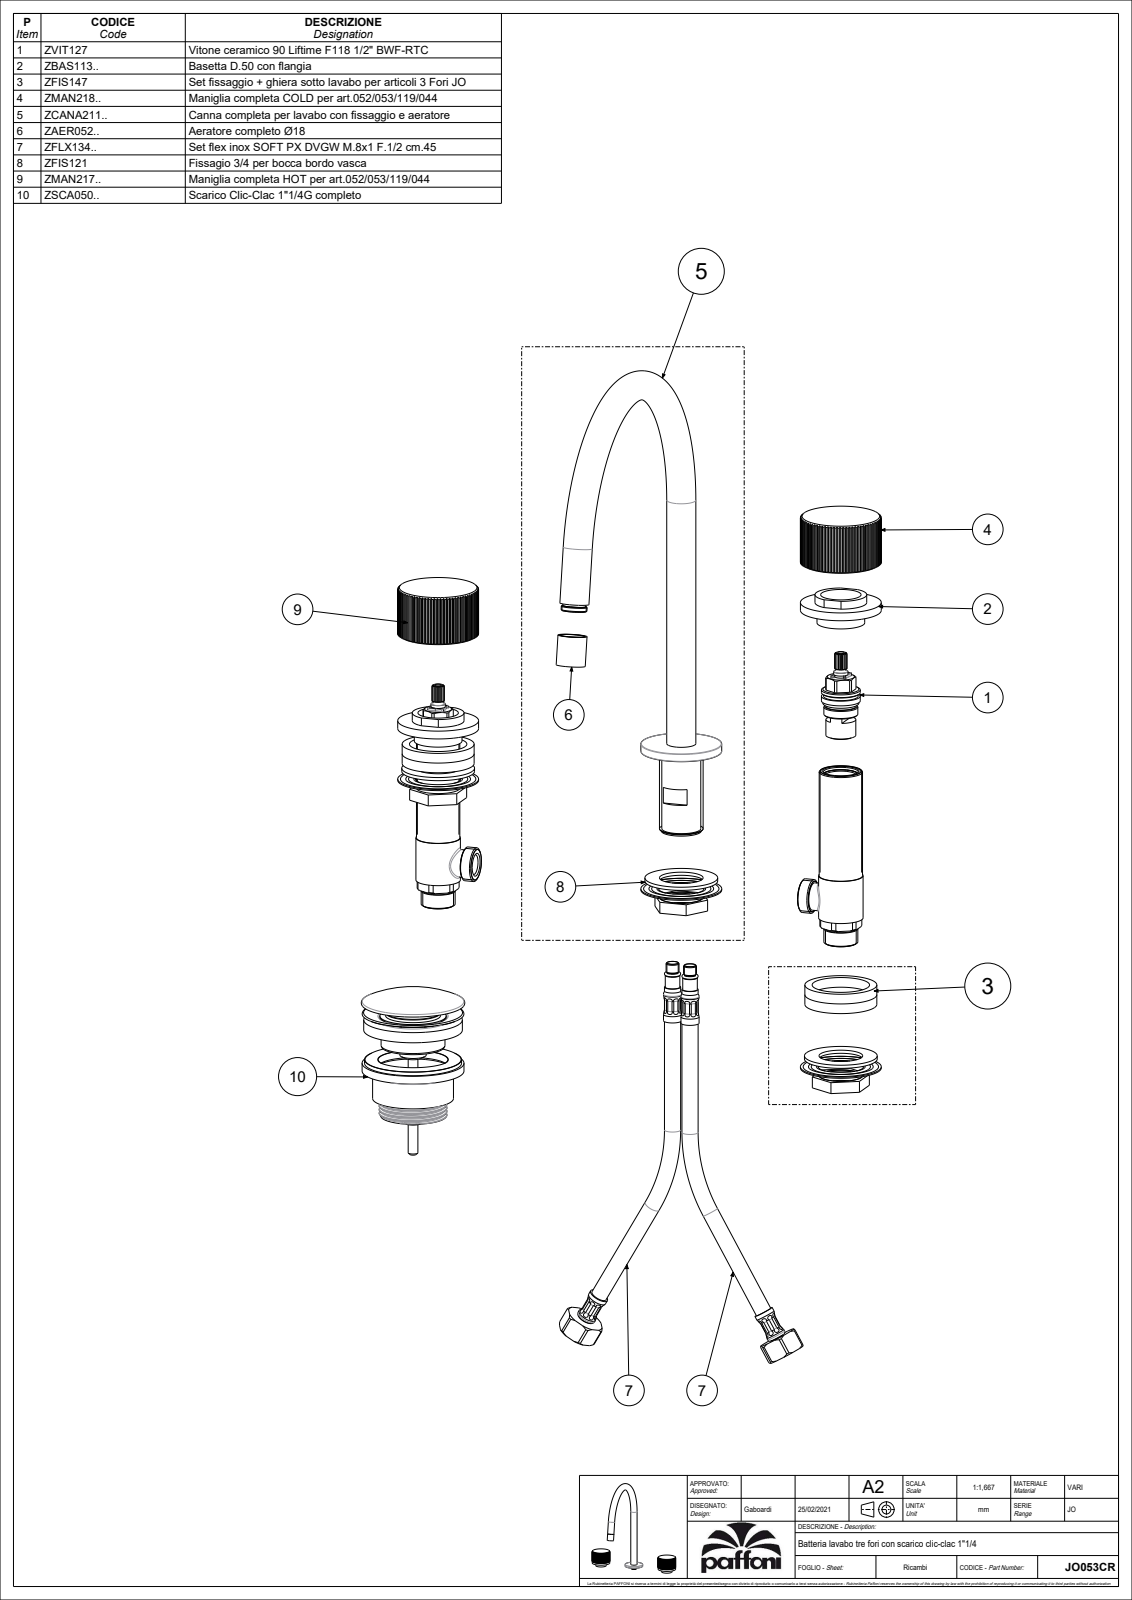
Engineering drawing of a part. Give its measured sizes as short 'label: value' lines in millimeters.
name: JO052CR
written by: CREO PARAMETRIC BY PTC INC, 2020044 (CONFIG_CONTROL_DESIGN)
unit: mm
bodies: 7 solids, 1210 faces (588 planar, 524 cylindrical, 98 other)
size: 290 × 264.31 × 231.59
volume: 121 281 mm³; area: 103 346 mm²
holes: 51× ⌀0.5, 5× ⌀15, 2× ⌀3, 2× ⌀3.3, 2× ⌀4.2, 2× ⌀4.25, 2× ⌀5.5, 2× ⌀8, 2× ⌀25, 2× ⌀41, 2× ⌀46.2, 2× ⌀47
bosses: 3× ⌀50, 2× ⌀44, 2× ⌀41.2, 2× ⌀24, 2× ⌀22, 2× ⌀21.4, 2× ⌀18, 2× ⌀8.8
rounds: 52× R0.2, 4× R1, 2× R9.4, 2× R16
face distances: 5, 33.7, 28.7, 34.66, 34.64, 2.5, 0.5, 3.7, 2, 10
hole spacings: 1.5, 3.35, 2.12, 4.74, 3, 4.24, 4.5, 3.36
